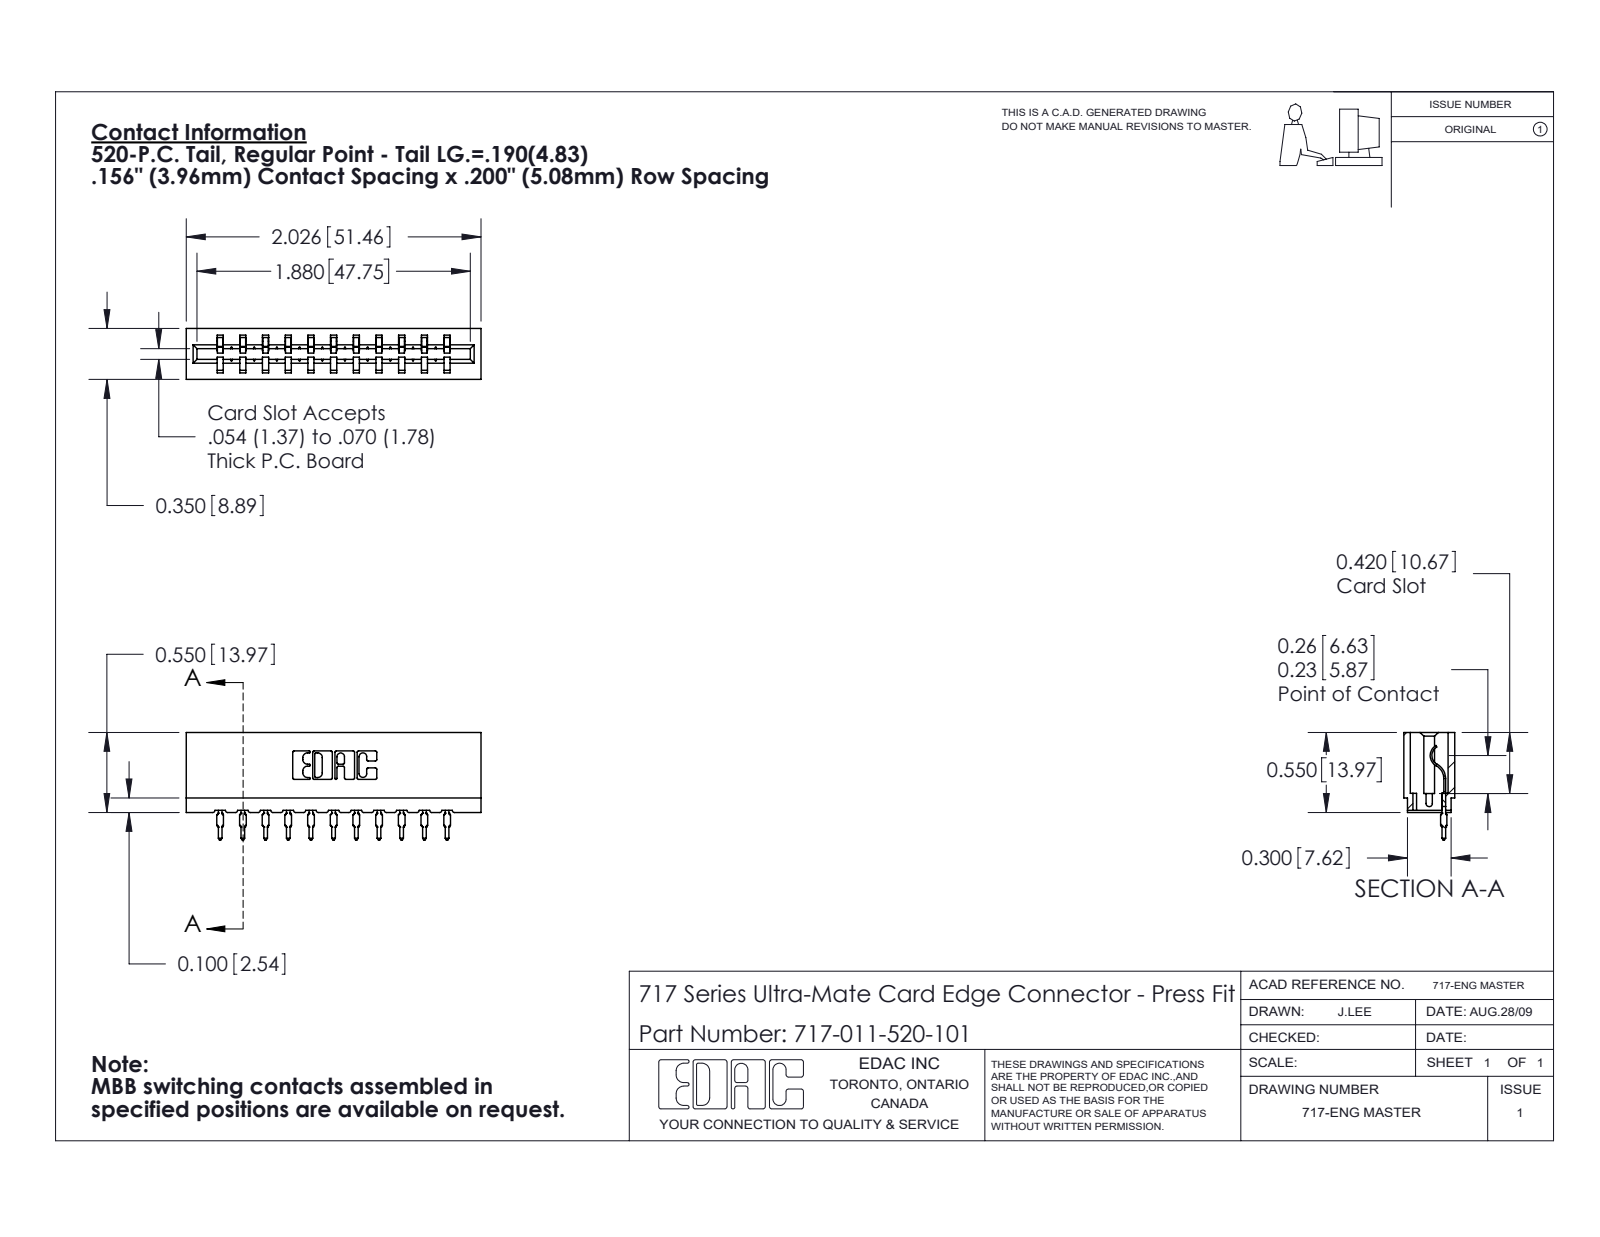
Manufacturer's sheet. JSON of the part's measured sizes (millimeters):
{"part_name": "717-011-520-101; 717 Part_Insulator Option - 06; 745-292-001_520", "step_written_by": "SolidWorks 2020 (CONFIG_CONTROL_DESIGN)", "units": "millimeters", "bodies": {"solids": 12, "faces": 1337, "planar": 802, "cylindrical": 249, "other": 286}, "overall_size": [51.5, 18.8, 8.9], "volume_mm3": 4470, "surface_area_mm2": 5865, "partial_cylinders_radius": [[0.3, 22], [0.4, 22], [0.5, 22], [0.2, 6], [0.8, 6], [0.1, 4], [0.3, 4], [0.7, 3]], "face_to_face_distances": [5.4, 4, 3.5, 11.9, 15.8, 8.9, 7.9, 5, 7.9, 1.1]}
